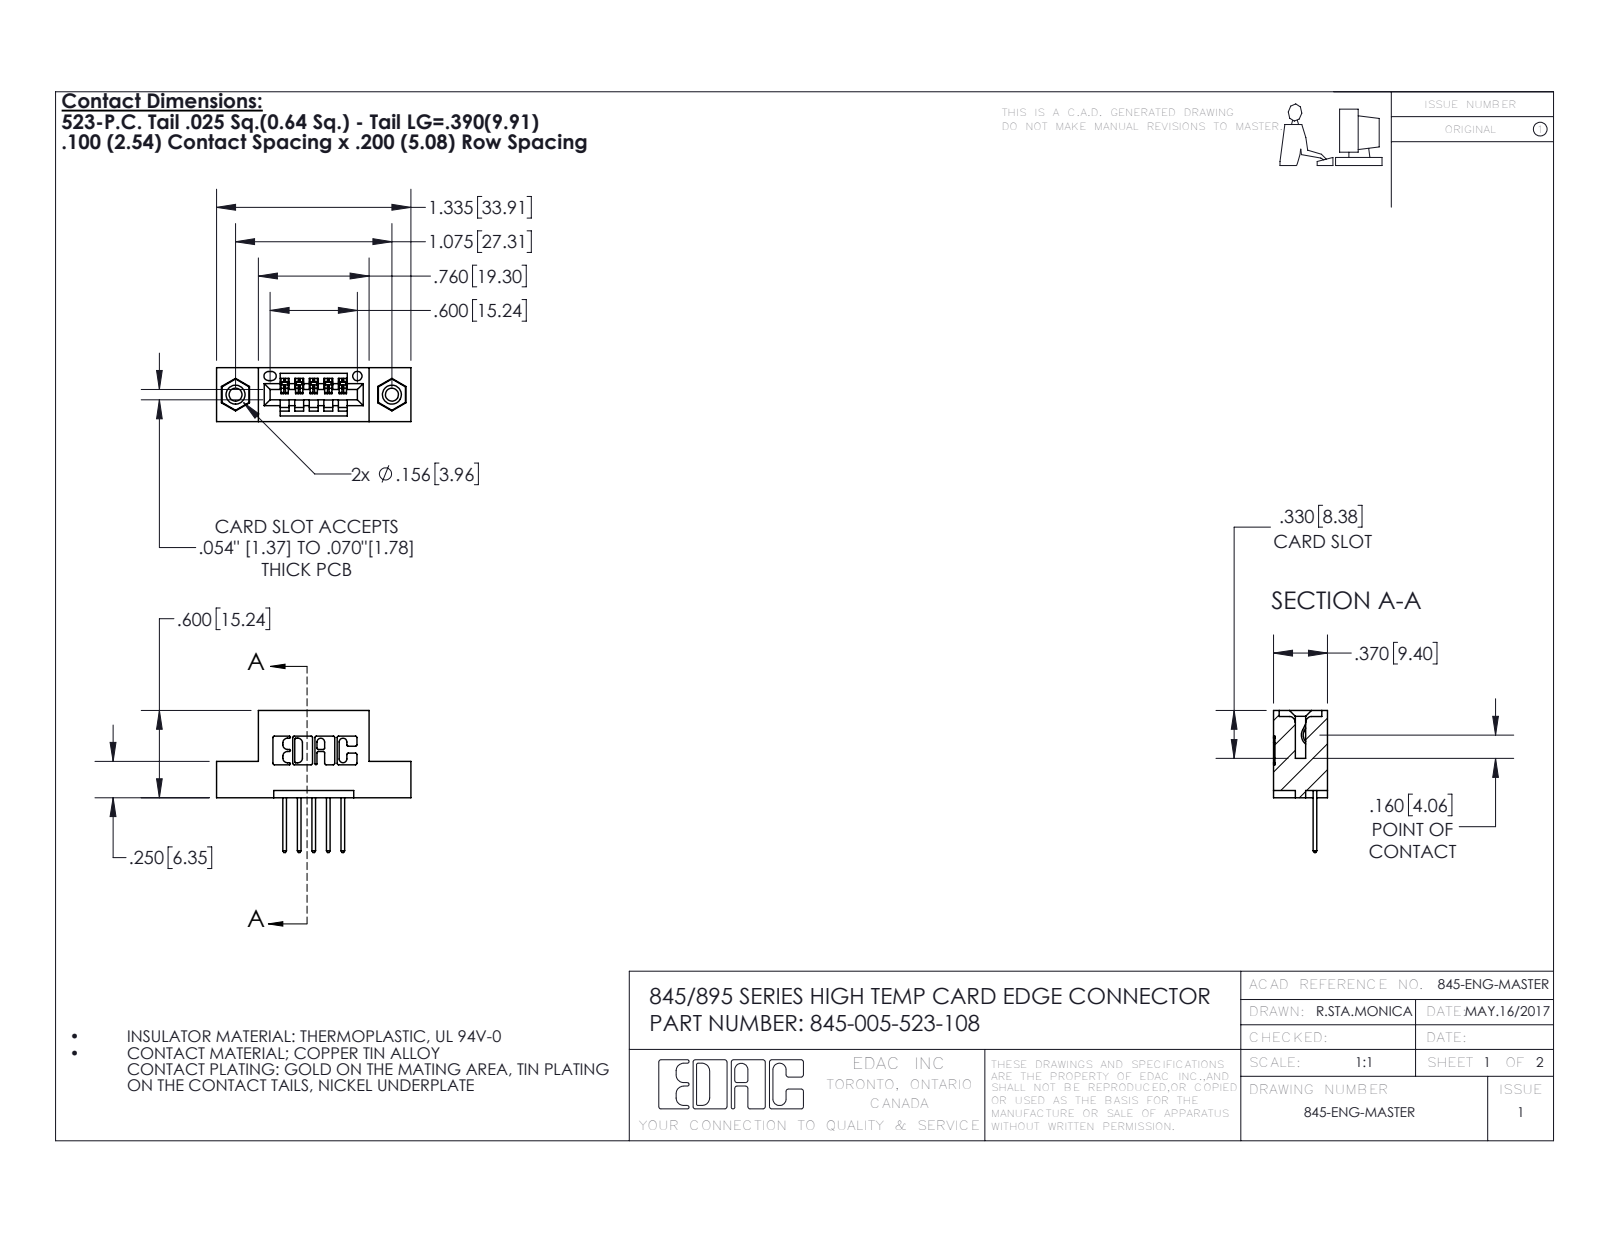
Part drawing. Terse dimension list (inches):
name: 345 Part_Flush Mounting Lugs - 0.156 Dia-TI; 345-250-001_345-250-003-102; 345-292-001_345-293-123; 345-005-523-108
written by: SolidWorks 2016 (CONFIG_CONTROL_DESIGN)
unit: in
bodies: 8 solids, 476 faces (312 planar, 148 cylindrical, 16 other)
size: 1.335 × 0.977 × 0.37
volume: 0.178 in³; area: 5.251 in²
holes: 2× ⌀0.089, 2× ⌀0.125, 2× ⌀0.156, 1× ⌀0.064
bosses: 2× ⌀0.155
rounds: 22× R0.01, 10× R0.006, 10× R0.01, 6× R0.007, 6× R0.031, 3× R0.026, 2× R0.031, 2× R0.04
face distances: 0.2, 0.37, 0.072, 0.298, 0.1, 0.025, 0.098, 0.272, 0.35, 0.25
hole spacings: 0.27, 0.847, 1.075
